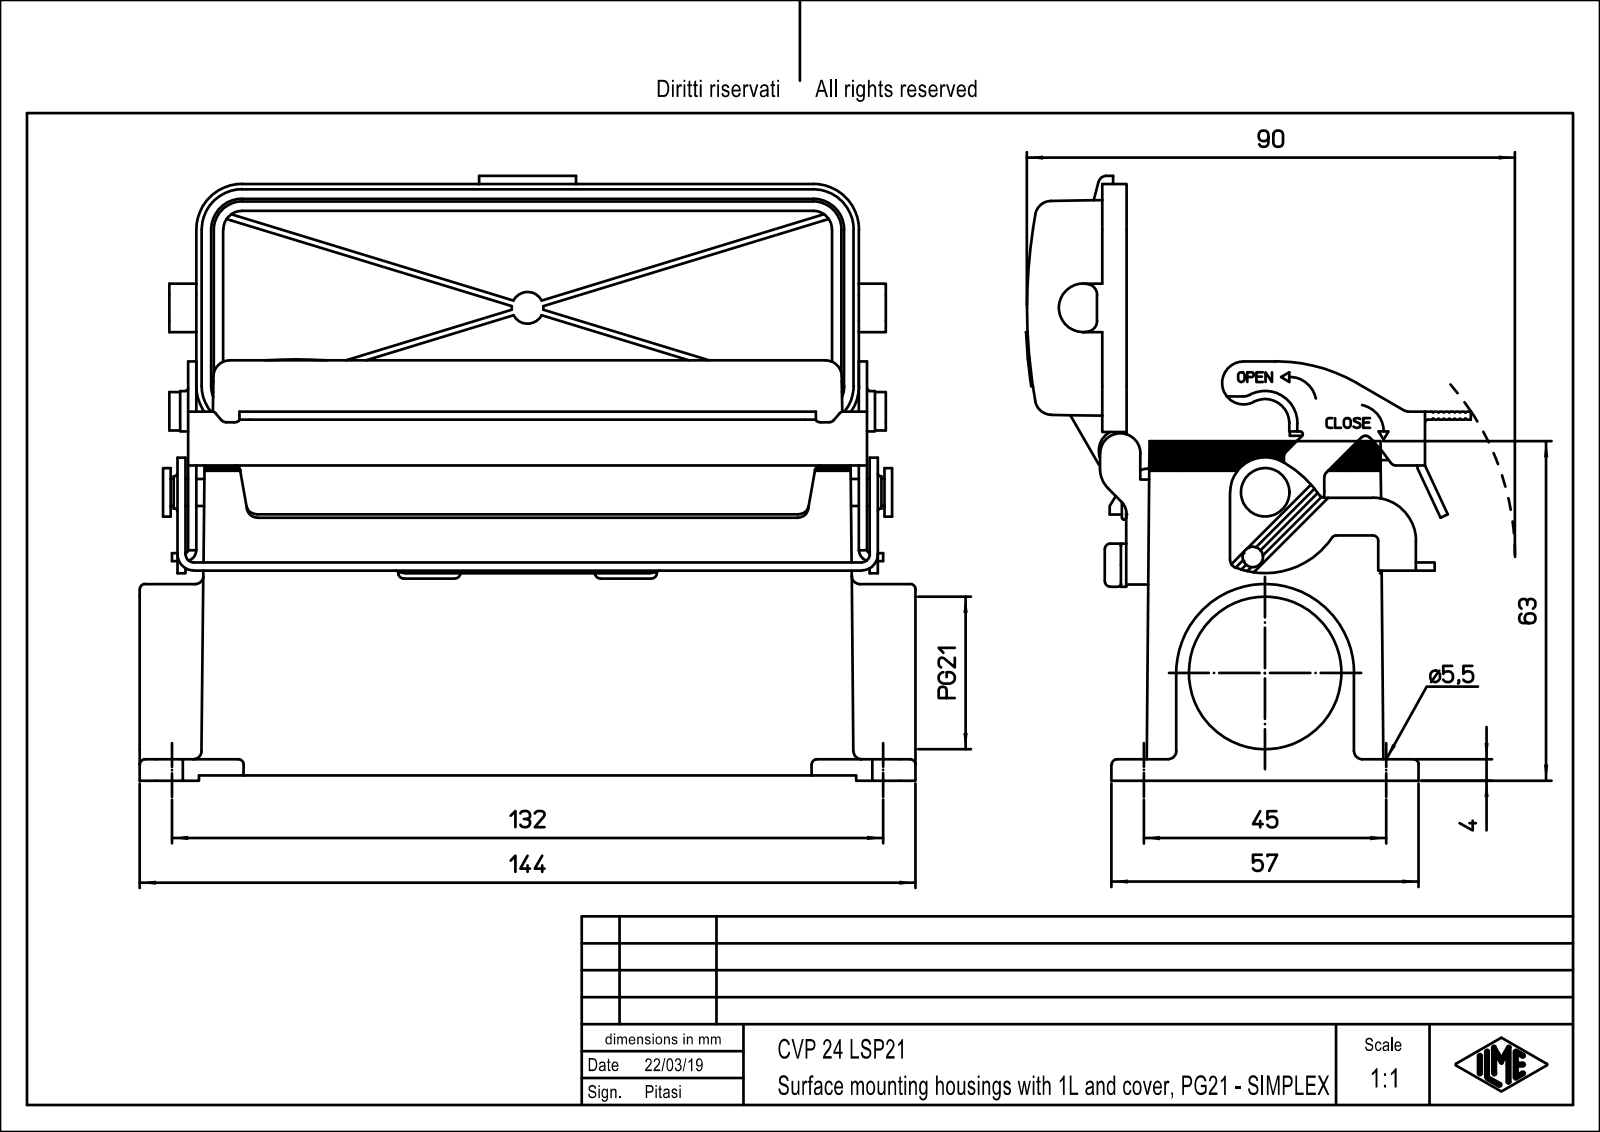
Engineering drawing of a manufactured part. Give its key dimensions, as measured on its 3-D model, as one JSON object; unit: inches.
{"part_name": "CVP_24_LSP21", "step_written_by": "PTC Creo Elements/Direct Modeling 19.0E 27-Jun-2016 (C) Parametric Technology GmbH (AUTOMOTIVE_DESIGN)", "units": "inches", "bodies": {"solids": 1, "faces": 616, "planar": 385, "cylindrical": 207, "other": 24}, "overall_size": [5.669, 4.438, 3.138], "volume_in3": 9.291, "surface_area_in2": 145.1, "round_holes": [[0.097, 4], [0.118, 4], [0.217, 4], [0.818, 1], [1.114, 1]], "round_bosses_or_shafts": [[0.031, 3], [0.354, 1], [0.331, 1], [0.315, 1], [0.236, 1], [0.197, 1], [0.094, 1]], "partial_cylinders_radius": [[0.079, 20], [0.118, 15], [0.059, 8], [0.138, 7], [0.039, 5], [0.236, 5], [0.02, 4], [0.071, 4]], "face_to_face_distances": [0.157, 1.594, 1.752, 1.437, 0.059, 0.463, 0.079, 1.587, 4.744, 2.765], "hole_center_spacings": [0.655, 1.521, 4.659, 4.857, 1.063, 1.772, 4.094, 4.23]}
